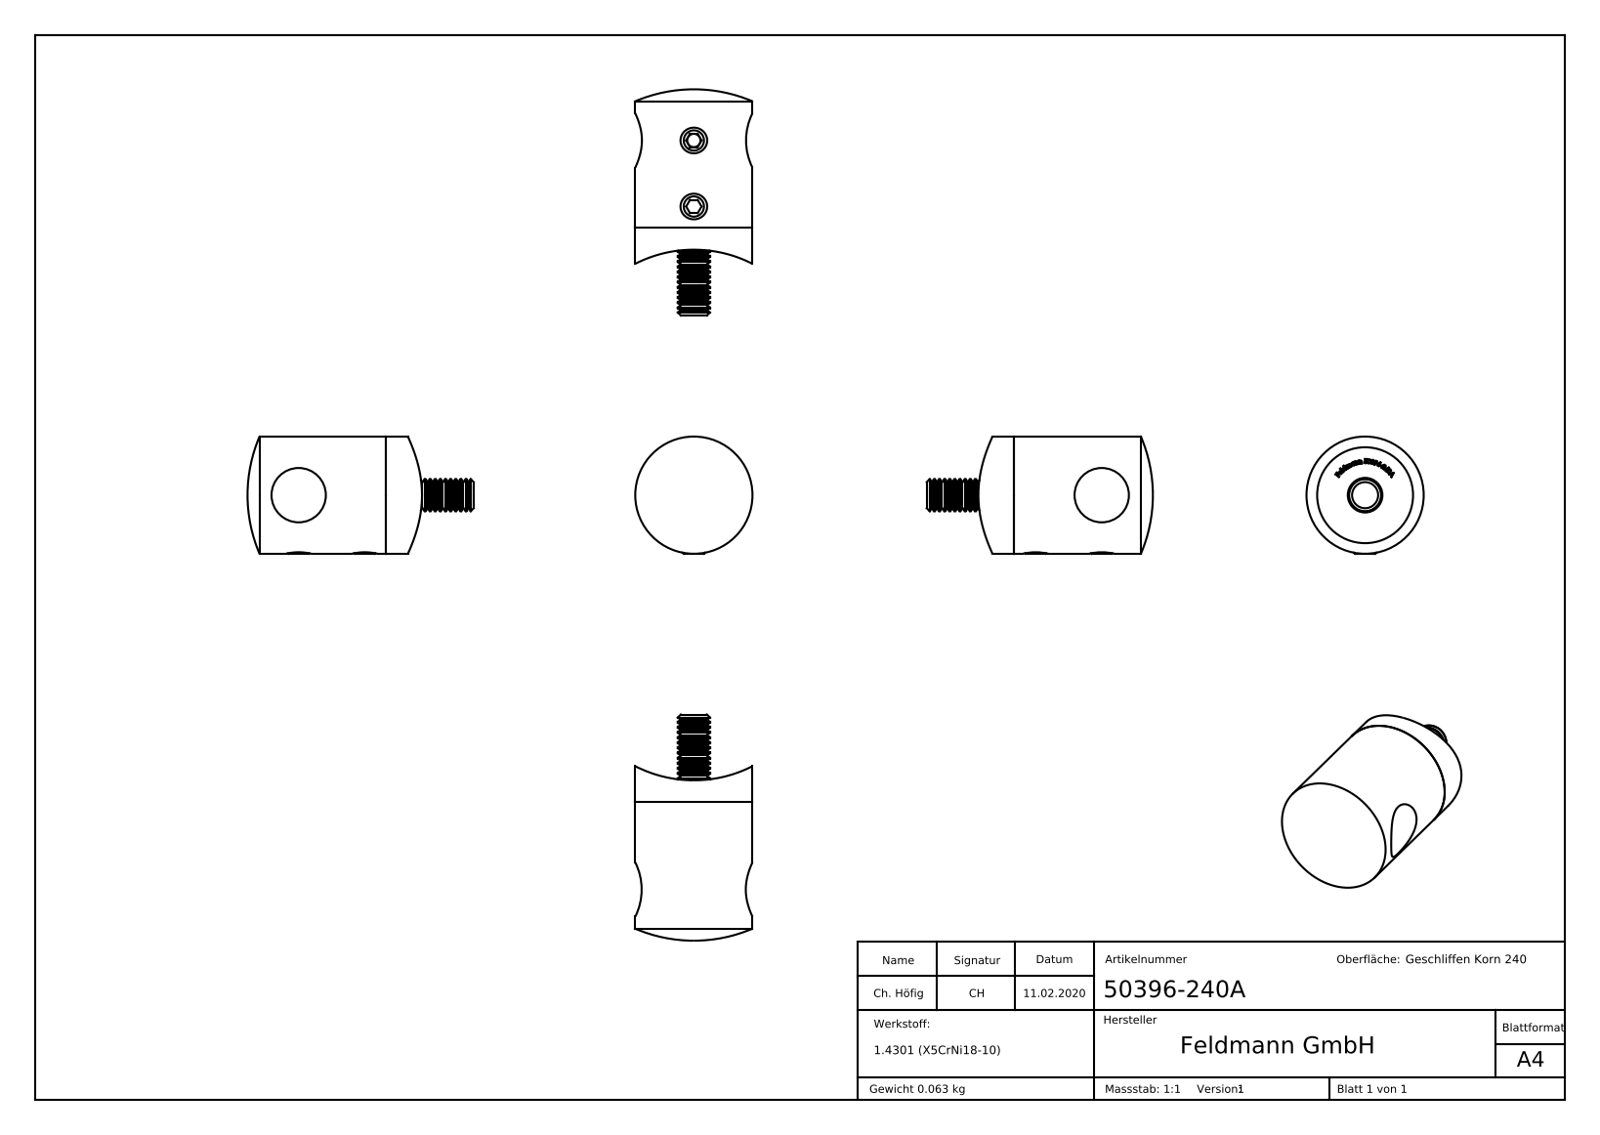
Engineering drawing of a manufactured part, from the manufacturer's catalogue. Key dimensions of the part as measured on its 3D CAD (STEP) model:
Part name (STEP PRODUCT): DIN914; Querstabhalter Teil1 Konfig; Querstabhalter Teil1 Konfig_50XXX-240A Teil1 10,2; DIN913_DIN 913 M5x5 (+7 more)
STEP written by: SolidWorks 2015 (CONFIG_CONTROL_DESIGN)
Units: millimetres
Bodies: 5 solids, 380 faces (174 planar, 36 cylindrical, 170 other)
Overall size (bounding box): 70 × 42.45 × 22
Volume: 8 661 mm³ · Surface area: 6 113 mm²
Round holes (diameter × count): ⌀4.2 ×2, ⌀6.5 ×1, ⌀10.2 ×1, ⌀12 ×1, ⌀18 ×1
Round bosses / shafts (diameter × count): ⌀5 ×2, ⌀22 ×1, ⌀11.9 ×1, ⌀11.57 ×1, ⌀6 ×1
Partial cylindrical surfaces — rounded edges, fillets, slot ends (radius × count): R24.15 ×1
Main face-to-face distances: 2.1, 10.65, 8.55, 2.5, 9.6, 7.5, 1.05, 14.35, 16.45, 23.95
Hole centre spacings: 12.4
